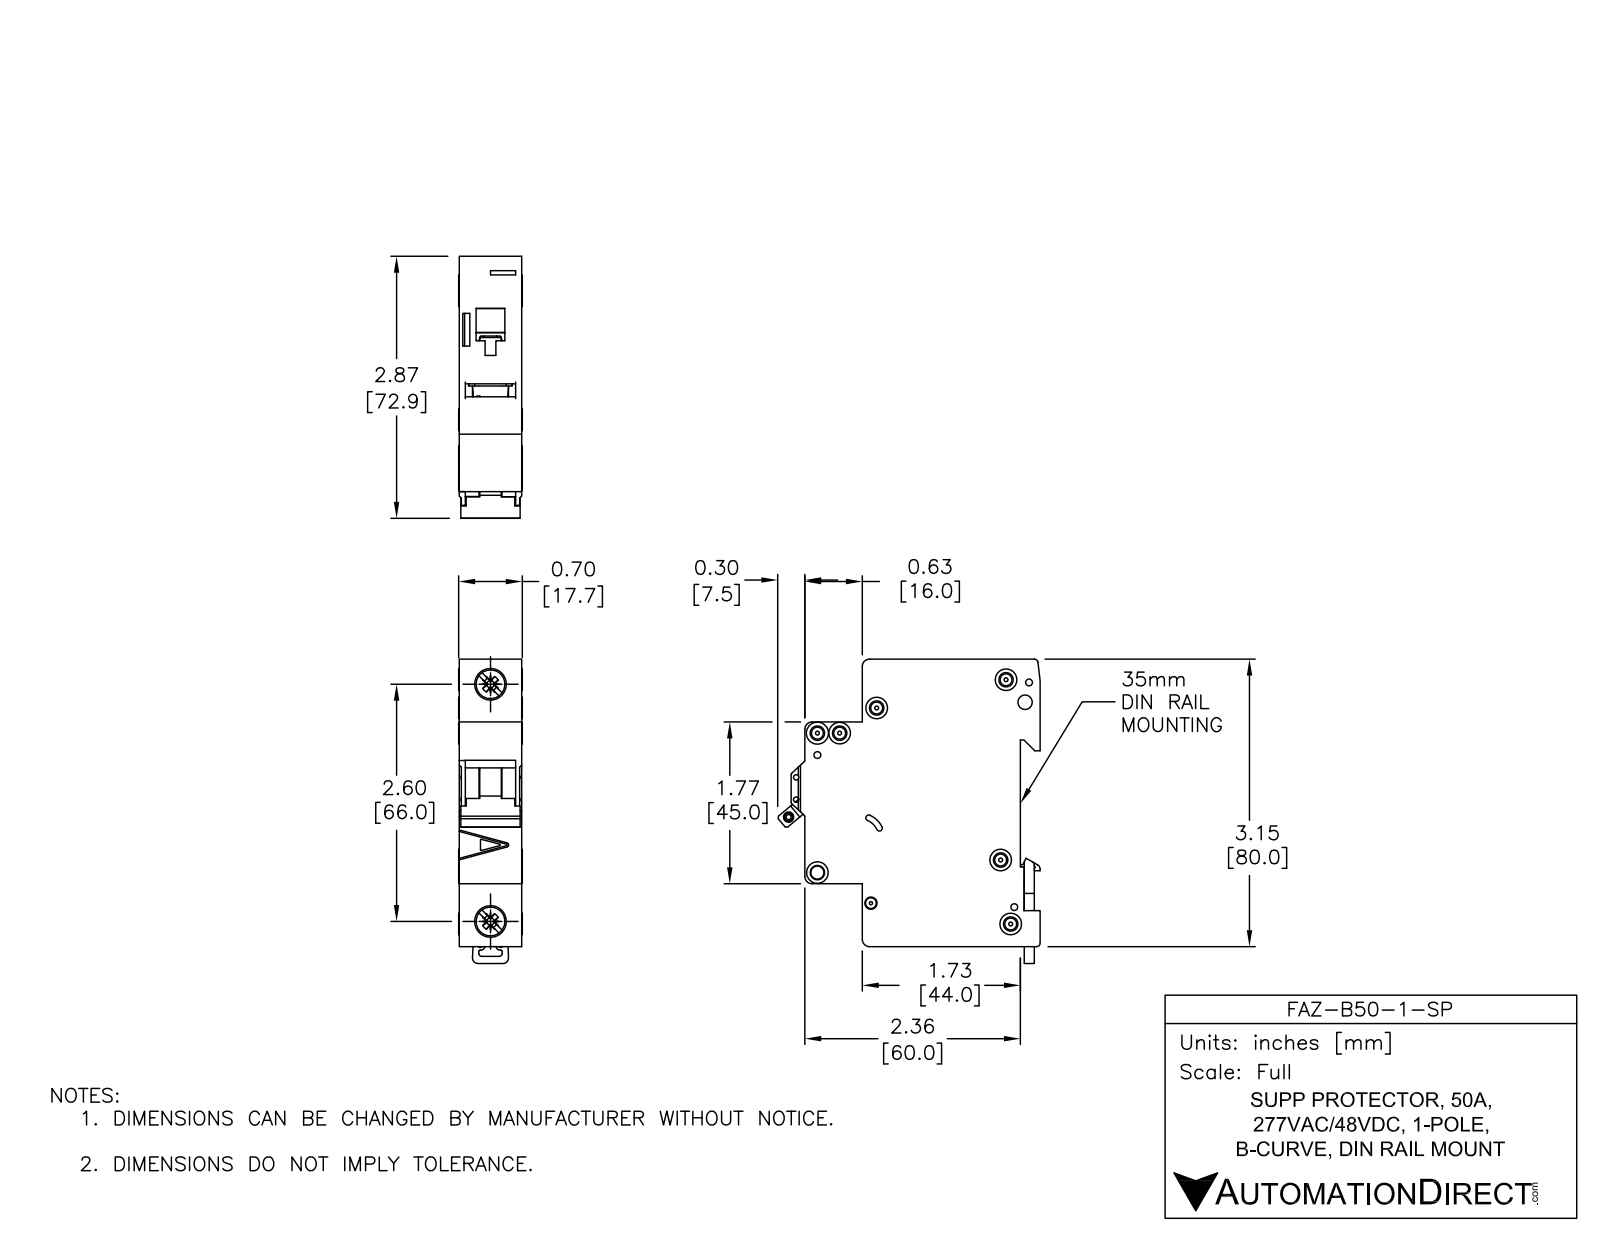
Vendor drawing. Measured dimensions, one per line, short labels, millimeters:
name: FAZ-B50-1-SP
written by: SolidWorks 2014 (AUTOMOTIVE_DESIGN)
unit: mm
bodies: 5 solids, 558 faces (235 planar, 202 cylindrical, 121 other)
size: 84.78 × 73.04 × 17.7
volume: 74 935 mm³; area: 19 545 mm²
holes: 6× ⌀3.6, 3× ⌀1.9, 2× ⌀1.09, 2× ⌀1.5, 2× ⌀4, 2× ⌀7.15, 1× ⌀2.15, 1× ⌀2.2, 1× ⌀2.55, 1× ⌀3.3, 1× ⌀3.4
bosses: 4× ⌀6, 2× ⌀8.2, 1× ⌀2.5
rounds: 30× R0.25, 13× R0.5, 8× R2, 5× R0.2, 4× R1, 2× R0.8, 2× R3, 1× R1.5
face distances: 17.5, 79.48, 5.5, 49.5, 44, 65.5, 60, 16, 1.75, 15.75
hole spacings: 6.2, 13.64, 4.81, 5.19, 5.61, 6.1, 6.44, 8.19
